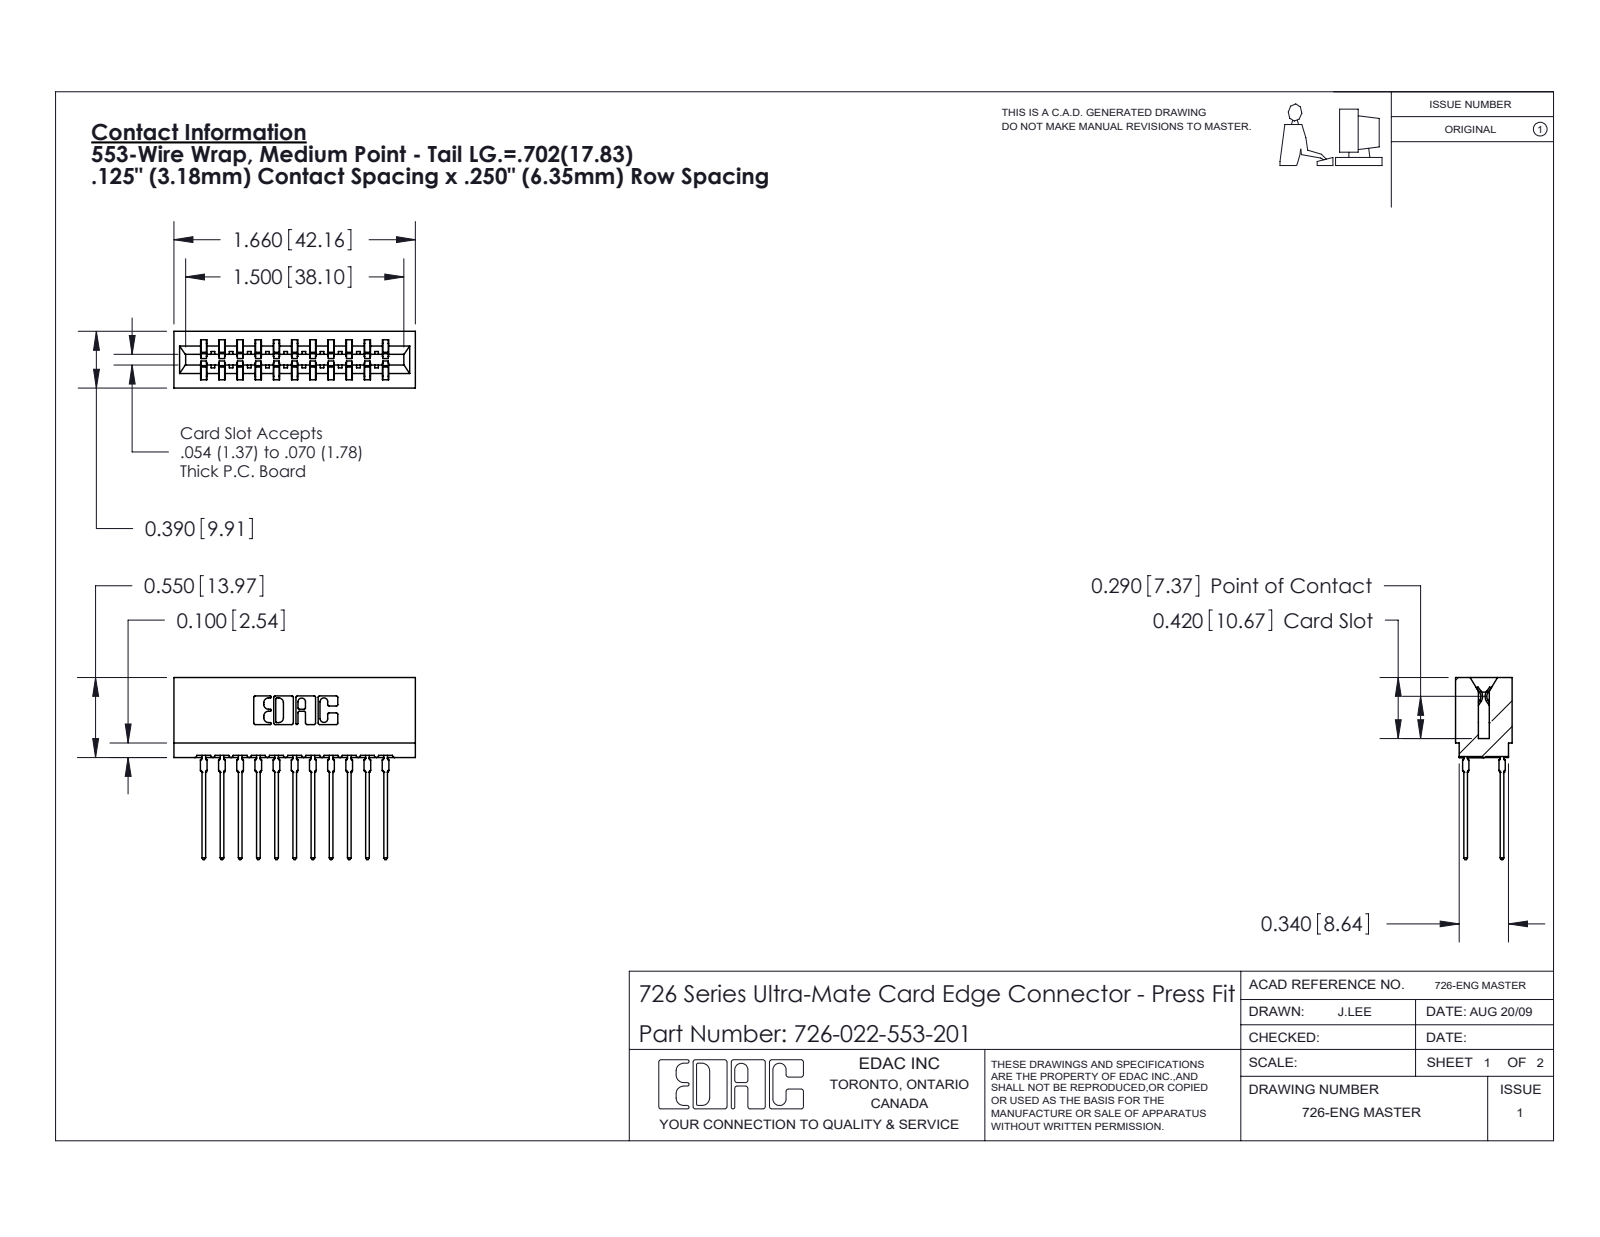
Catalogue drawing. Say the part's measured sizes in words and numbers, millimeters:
The part is named "726-022-553-201; 726 Part_.515 Slot Depth - 01; 746-292-001_553". Its 3-D file was written by "SolidWorks 2020 (CONFIG_CONTROL_DESIGN)". It is 23 solids with 2066 faces: 1067 planar, 427 cylindrical and 572 other. Overall it measures 42.2 by 31.8 by 9.9 millimeters. Its volume is 4 150 cubic millimeters and its surface area 6 800 square millimeters. Partial cylindrical surfaces (rounded edges, fillets, slot ends): 44 of radius 0.5, 22 of radius 0.3, 12 of radius 0.4, 8 of radius 0.1, 8 of radius 0.3, 6 of radius 0.2, 6 of radius 0.8, 3 of radius 0.7. The main face-to-face distances are 6.4, 8.5, 1.4, 2.1, 0.6, 7.8, 12.7, 19.1, 1.1, 3.2.
